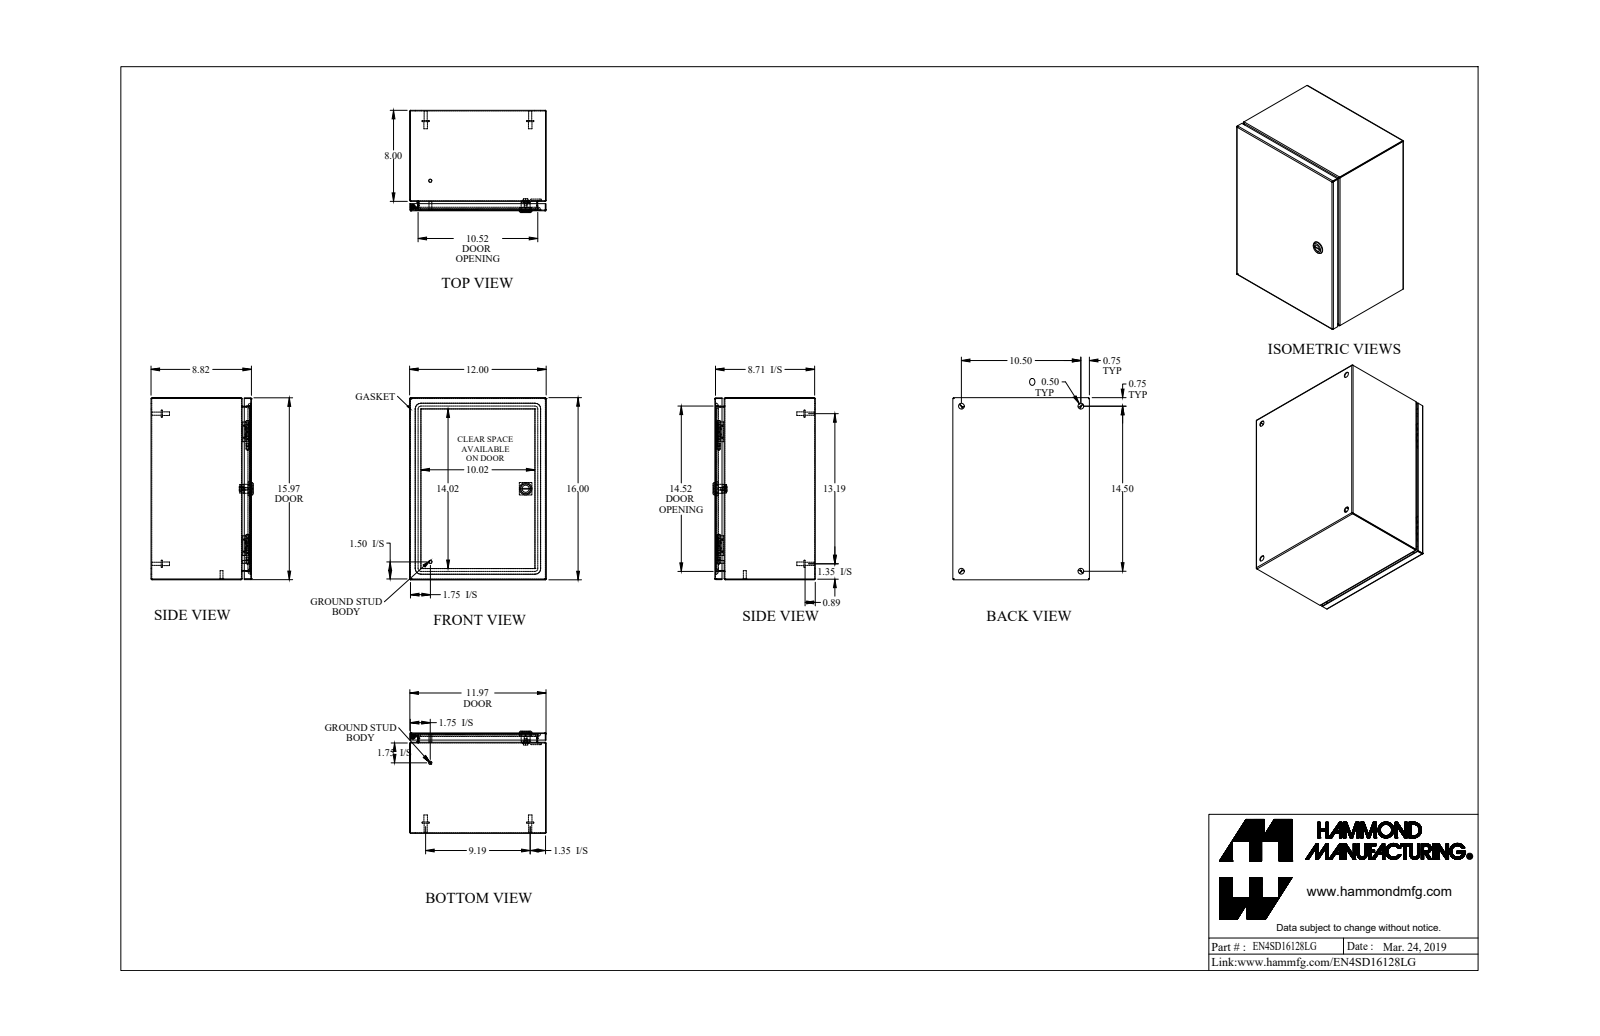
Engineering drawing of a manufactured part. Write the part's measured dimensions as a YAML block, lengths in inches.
part_name: "EN4SD16128LG_Default"
step_written_by: "SolidWorks 2019 (CONFIG_CONTROL_DESIGN)"
units: inches
bodies: {solids: 21, faces: 634, planar: 285, cylindrical: 213, other: 136}
overall_size: [16, 12, 8.982]
volume: 59.35
surface_area: 2008
round_holes:
  - {diameter: 0.5, count: 4}
  - {diameter: 0.172, count: 1}
  - {diameter: 0.232, count: 1}
  - {diameter: 0.24, count: 1}
  - {diameter: 0.242, count: 1}
  - {diameter: 0.625, count: 1}
  - {diameter: 0.785, count: 1}
round_bosses_or_shafts:
  - {diameter: 0.625, count: 4}
  - {diameter: 0.313, count: 4}
  - {diameter: 0.27, count: 4}
  - {diameter: 0.281, count: 2}
  - {diameter: 0.25, count: 2}
  - {diameter: 1.1, count: 1}
  - {diameter: 0.525, count: 1}
  - {diameter: 0.455, count: 1}
partial_cylinders:
  - {radius: 0.029, count: 21}
  - {radius: 0.086, count: 21}
  - {radius: 0.25, count: 16}
  - {radius: 19, count: 8}
  - {radius: 0.006, count: 4}
  - {radius: 0.062, count: 4}
  - {radius: 0.499, count: 4}
  - {radius: 0.125, count: 2}
face_to_face_distances: [0.057, 8.765, 11.943, 8.708, 8.822, 15.943, 11.886, 12, 15.886, 16]
hole_center_spacings: [10.5, 14.5, 17.902, 7.326, 7.327, 11.903, 11.904]
